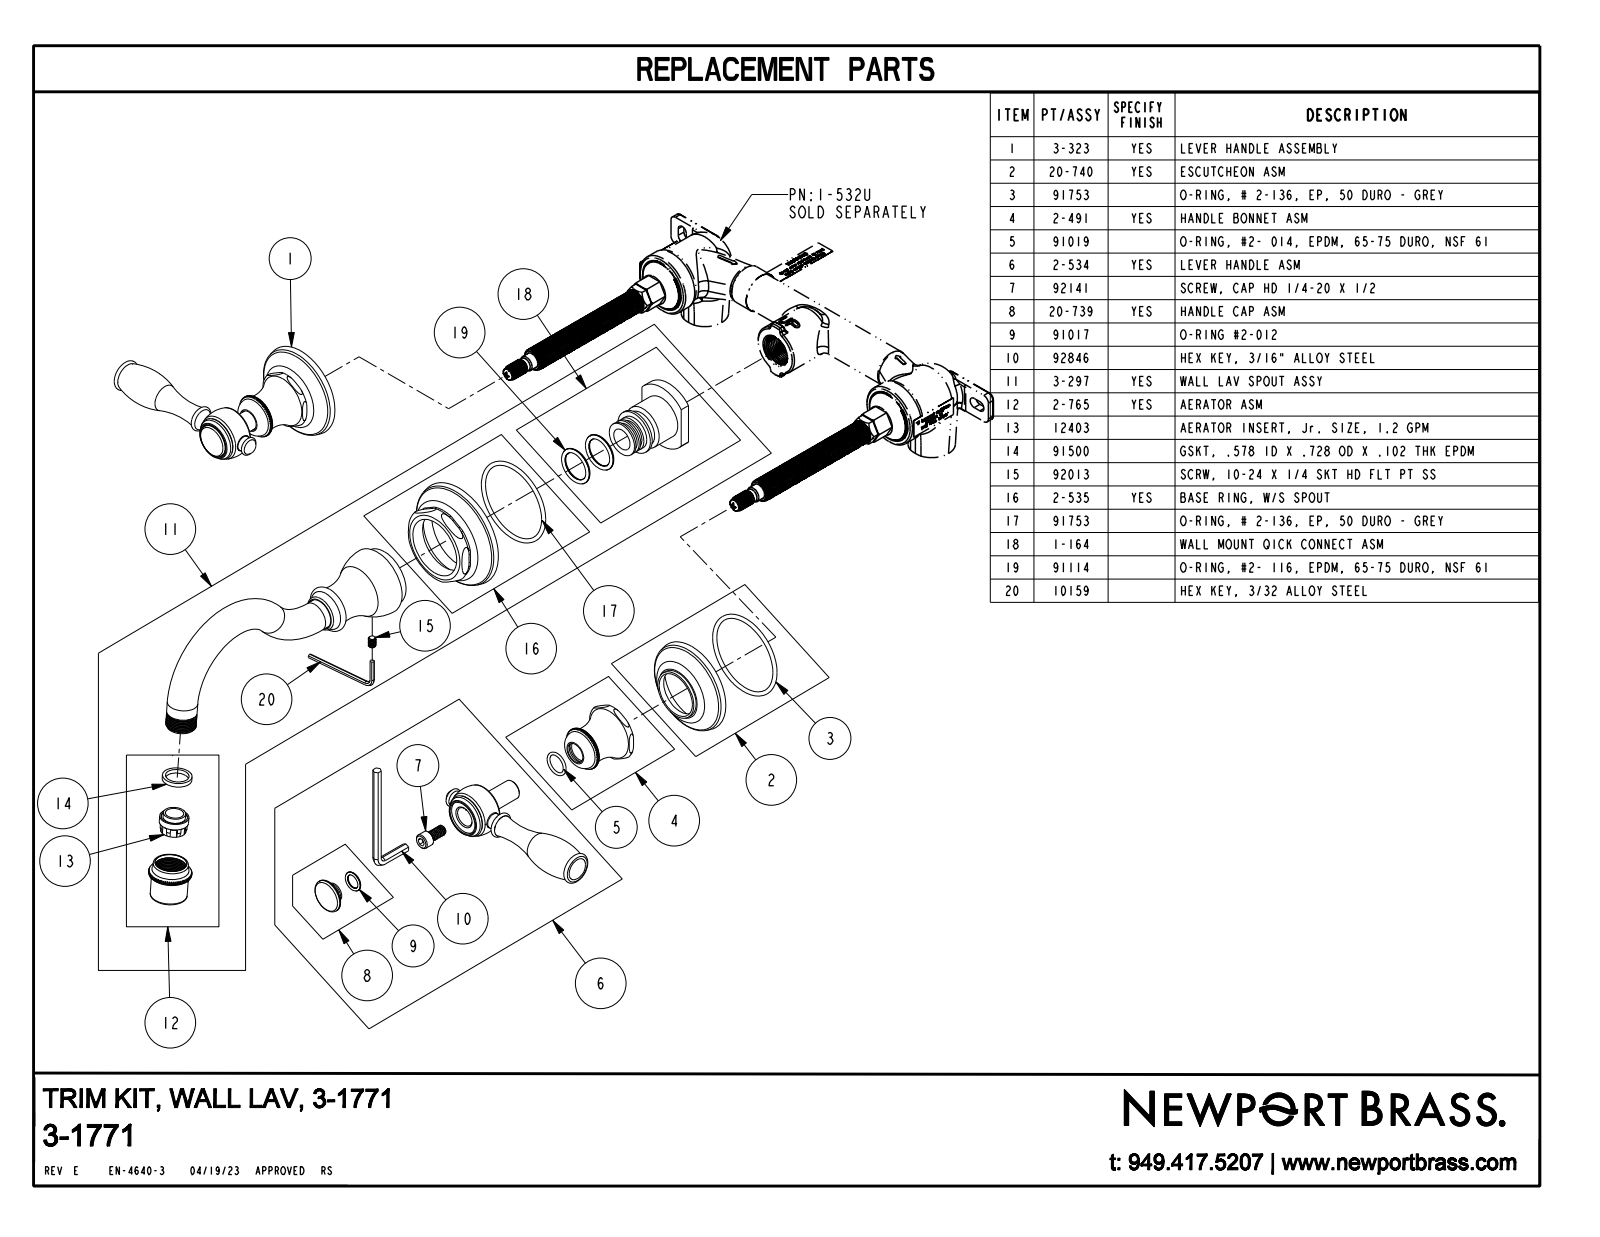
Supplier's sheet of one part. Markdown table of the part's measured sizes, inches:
| quantity | value |
| --- | --- |
| part name | 3-1771_SW0001 |
| STEP written by | CREO PARAMETRIC BY PTC INC, 2018400 (AUTOMOTIVE_DESIGN) |
| units | inches |
| bodies | 3 solids, 659 faces (457 planar, 34 cylindrical, 168 other) |
| overall size | 15.168 × 8.178 × 3.215 |
| volume | 18.63 in³ |
| surface area | 94.98 in² |
| round holes (diameter × count) | 0.855 × 2, 0.41 × 1 |
| round bosses / shafts (diameter × count) | 0.84 × 2, 0.75 × 2, 0.5 × 2, 0.91 × 1, 0.392 × 1 |
| main face-to-face distances | 2.29, 1.86, 1.726, 3.586, 0.352, 2.211, 1.375, 3.938, 6.533, 8.393 |
| hole center spacings | 7.876 |
